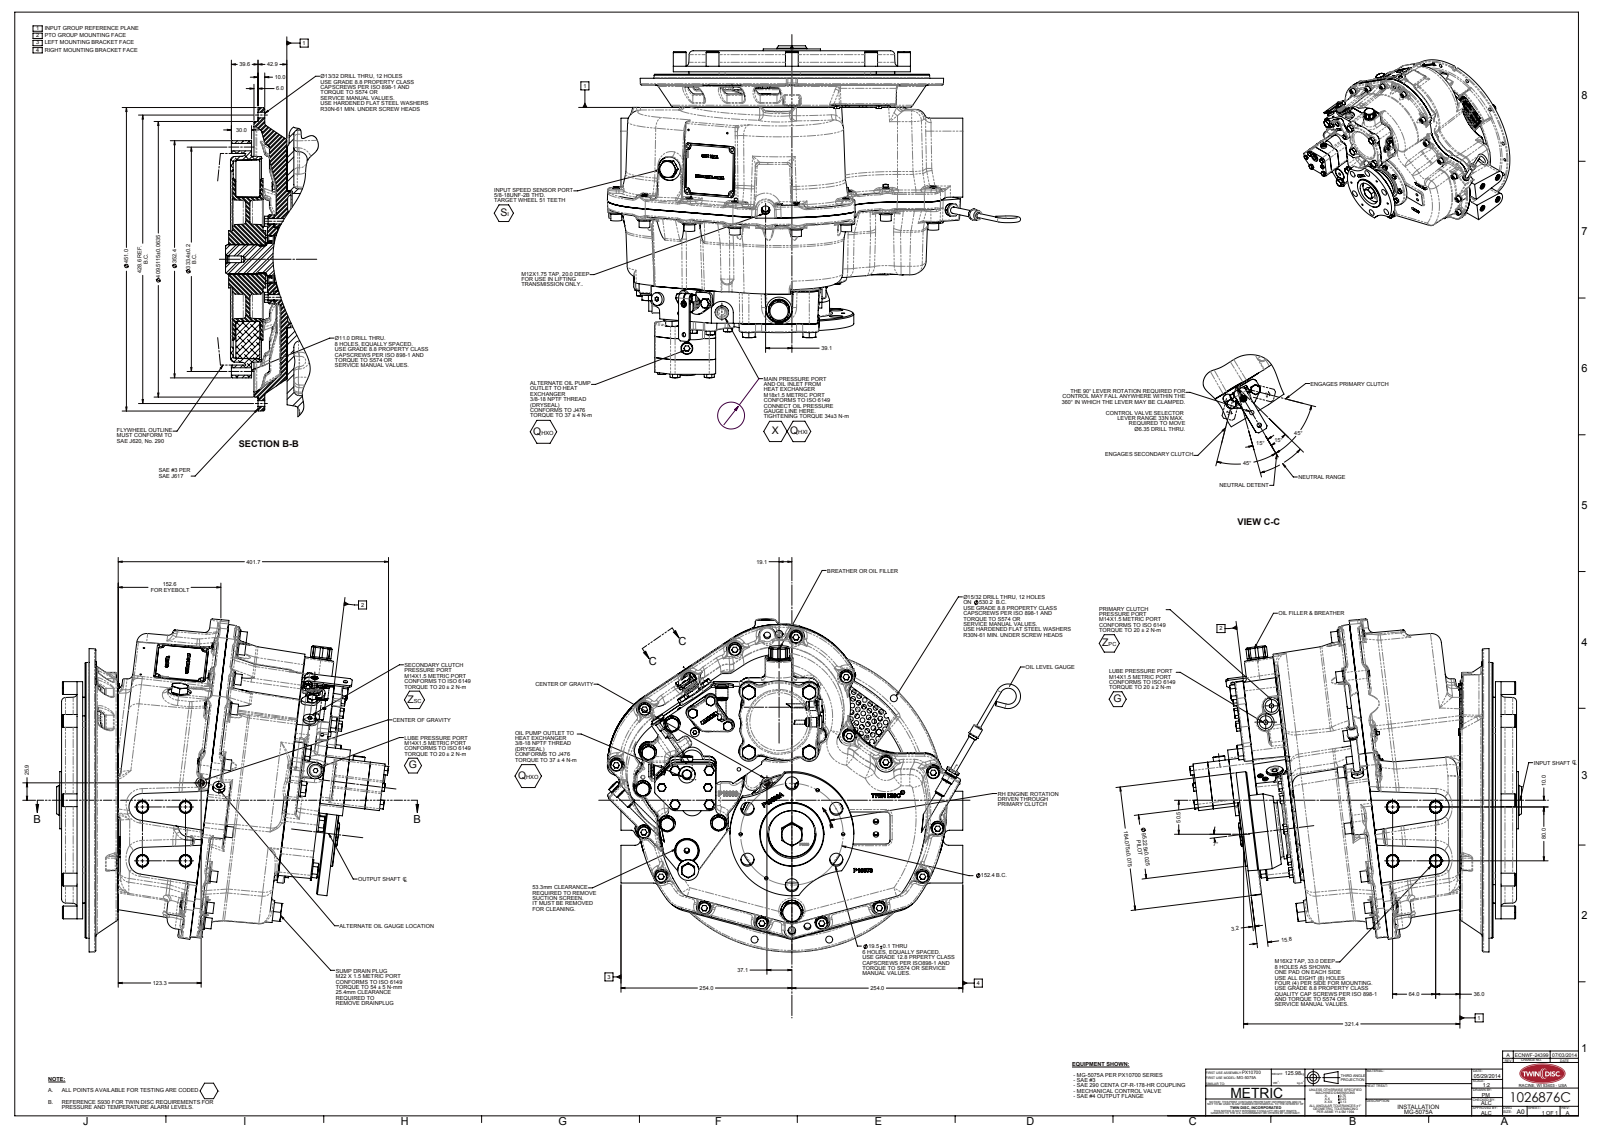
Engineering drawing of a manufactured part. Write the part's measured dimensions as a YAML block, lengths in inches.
part_name: "1026876C"
step_written_by: "SolidWorks 2010 (AUTOMOTIVE_DESIGN)"
units: inches
bodies: {solids: 0, faces: 8051, planar: 3338, cylindrical: 2106, other: 2607}
overall_size: [24.175, 19.485, 19.42]
round_holes:
  - {diameter: 0.276, count: 46}
  - {diameter: 0.394, count: 14}
  - {diameter: 0.406, count: 12}
  - {diameter: 0.433, count: 8}
  - {diameter: 0.098, count: 6}
  - {diameter: 0.315, count: 6}
  - {diameter: 0.768, count: 6}
  - {diameter: 0.197, count: 4}
  - {diameter: 0.346, count: 4}
  - {diameter: 0.65, count: 4}
  - {diameter: 0.741, count: 4}
  - {diameter: 0.209, count: 3}
round_bosses_or_shafts:
  - {diameter: 0.781, count: 17}
  - {diameter: 0.63, count: 17}
  - {diameter: 0.748, count: 12}
  - {diameter: 0.394, count: 11}
  - {diameter: 0.625, count: 9}
  - {diameter: 0.945, count: 5}
  - {diameter: 5, count: 3}
  - {diameter: 0.25, count: 3}
partial_cylinders:
  - {radius: 0.668, count: 274}
  - {radius: 0.05, count: 192}
  - {radius: 0.031, count: 135}
  - {radius: 0.079, count: 132}
  - {radius: 0.157, count: 53}
  - {radius: 0.098, count: 39}
  - {radius: 0.315, count: 28}
  - {radius: 0.059, count: 27}
face_to_face_distances: [0.017, 0.348, 0.365, 0.015, 0.018, 4.643, 4.644, 4.659, 4.66, 0.394]
hole_center_spacings: [8.437, 4.37, 5.996, 10.689, 11.932, 14.614, 16.3, 2.7]
